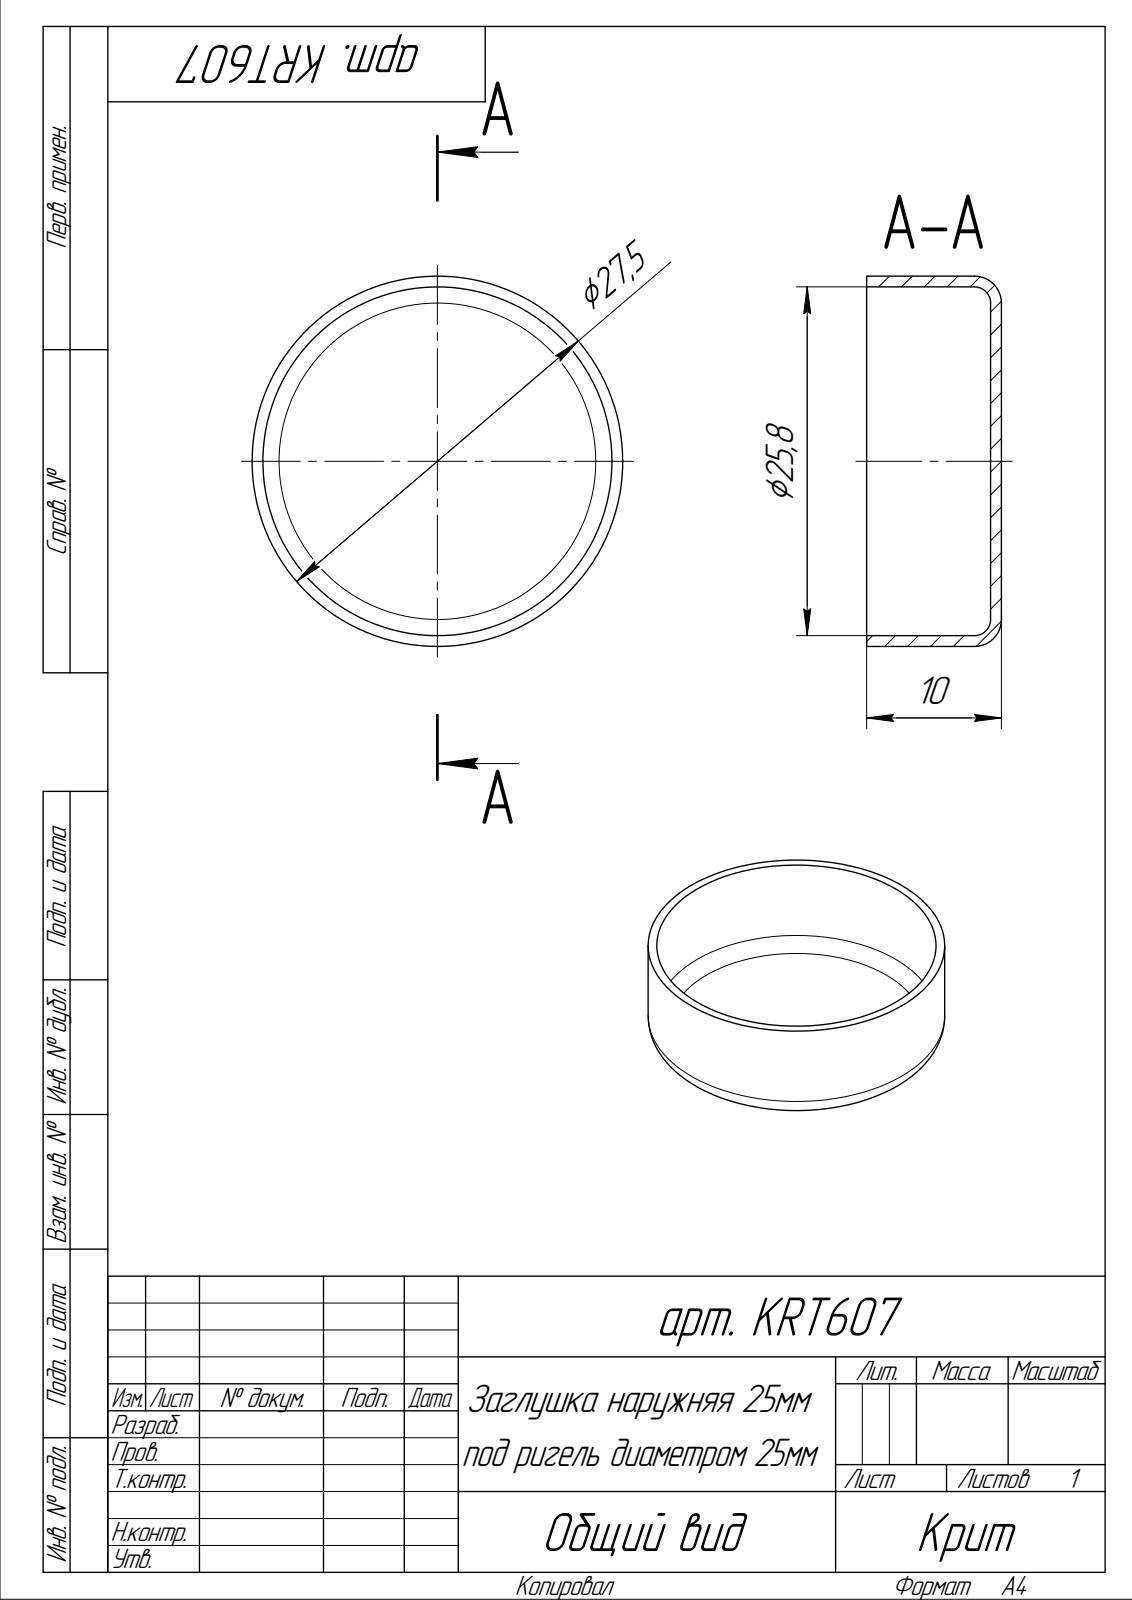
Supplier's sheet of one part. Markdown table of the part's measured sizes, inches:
| quantity | value |
| --- | --- |
| part name | Деталь |
| STEP written by | ASCON Math Kernel (AUTOMOTIVE_DESIGN) |
| units | inches |
| bodies | 1 solid, 7 faces (3 planar, 2 cylindrical, 2 other) |
| overall size | 1.083 × 1.083 × 0.394 |
| volume | 0.064 in³ |
| surface area | 4.157 in² |
| round holes (diameter × count) | 1.02 × 1 |
| round bosses / shafts (diameter × count) | 1.083 × 1 |
| main face-to-face distances | 0.031, 0.394, 0.362 |
